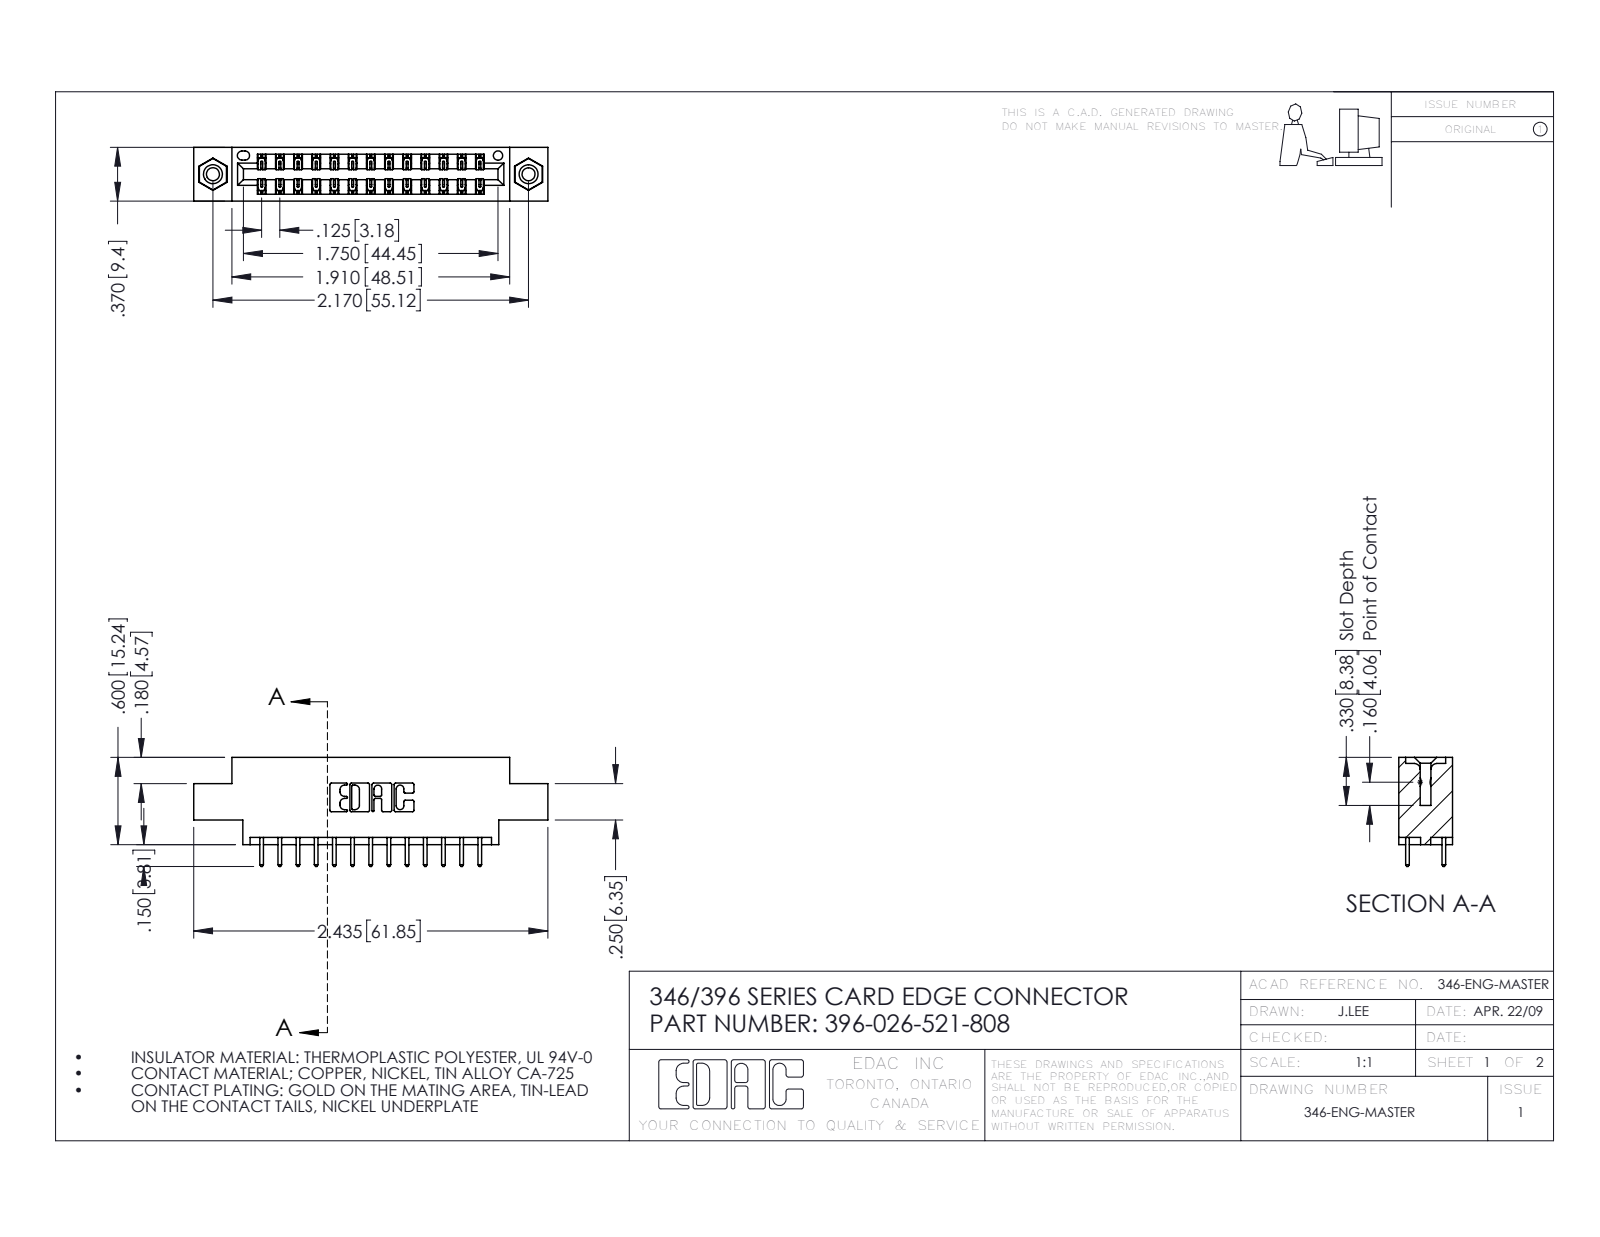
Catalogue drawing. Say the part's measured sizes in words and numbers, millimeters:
The part is named "346 Part_0.170 Offset - 0.156 Dia-TI; 345-292-001_345-293-121; 345-250-001_345-250-003-102; 396-026-521-808". Its 3-D file was written by "SolidWorks 2016 (CONFIG_CONTROL_DESIGN)". It is 29 solids with 1538 faces: 1022 planar, 500 cylindrical and 16 other. Overall it measures 61.8 by 19.1 by 9.4 millimeters. Its volume is 5 640 cubic millimeters and its surface area 7 419 square millimeters. Round holes: 2 of diameter 2.3, 2 of diameter 3.2, 2 of diameter 4, 1 of diameter 1.6. Round bosses or shafts: 2 of diameter 3.9. Partial cylindrical surfaces (rounded edges, fillets, slot ends): 39 of radius 0.2, 26 of radius 0.3, 22 of radius 0.3, 6 of radius 0.2, 6 of radius 0.8, 3 of radius 0.7, 2 of radius 0.4, 2 of radius 0.6. The main face-to-face distances are 1.2, 8.2, 6.4, 9.4, 1.8, 7.6, 0.6, 7, 5.6, 3.8. The hole center spacings are 6.2, 49.9, 55.1.
